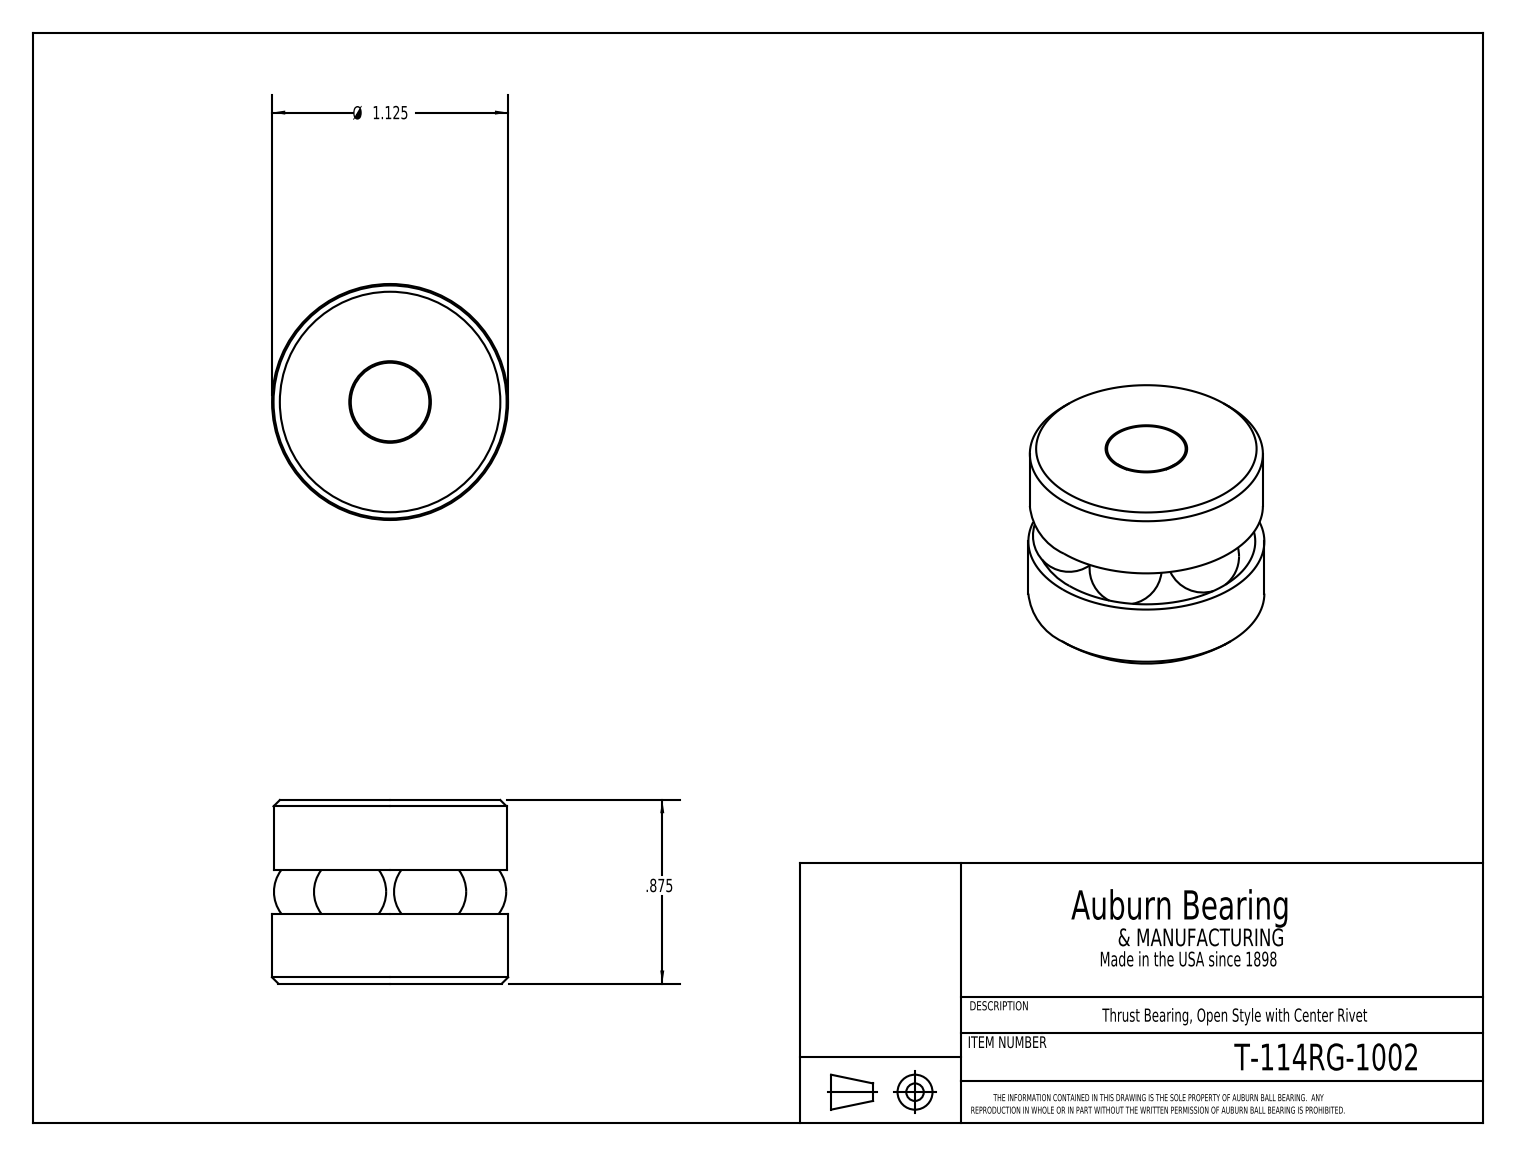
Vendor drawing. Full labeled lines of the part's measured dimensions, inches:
Part name (STEP PRODUCT): T-114RG_T-114RG-1002
STEP written by: SolidWorks 2016 (CONFIG_CONTROL_DESIGN)
Units: inches
Bodies: 9 solids, 27 faces (8 planar, 5 cylindrical, 14 other)
Overall size (bounding box): 1.125 × 1.125 × 0.875
Volume: 0.719 in³ · Surface area: 9.616 in²
Round holes (diameter × count): ⌀0.166 ×1
Round bosses / shafts (diameter × count): ⌀1.125 ×1, ⌀1.111 ×1, ⌀0.156 ×1
Main face-to-face distances: 0.875, 0.334, 0.541, 0.206, 0.875, 0.541, 0.335
